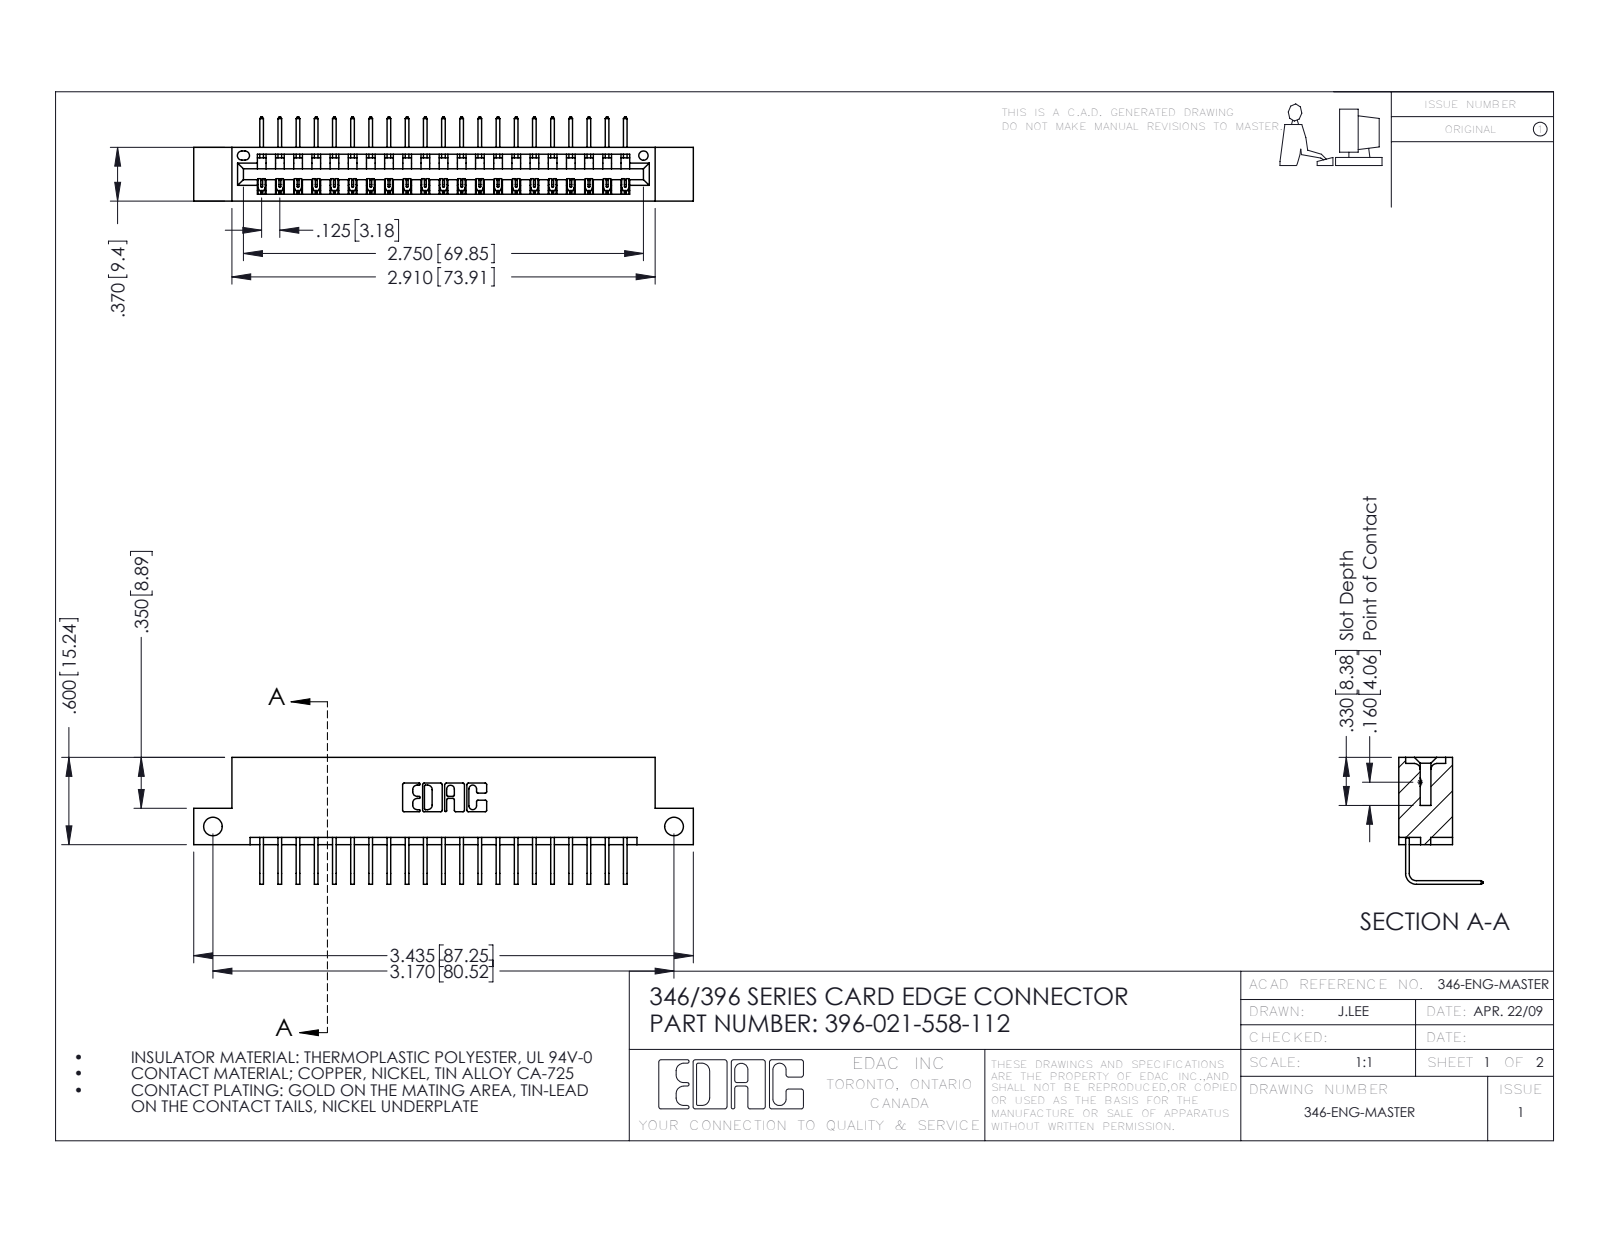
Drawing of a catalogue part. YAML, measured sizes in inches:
part_name: "345-292-001_558 Tail - 2; 346 Part_Flush Mounting Lugs - Side Mount; 396-021-558-112"
step_written_by: "SolidWorks 2016 (CONFIG_CONTROL_DESIGN)"
units: inches
bodies: {solids: 22, faces: 1382, planar: 958, cylindrical: 424, other: 0}
overall_size: [3.435, 0.873, 0.58]
volume: 0.5
surface_area: 15.94
round_holes:
  - {diameter: 0.128, count: 2}
  - {diameter: 0.064, count: 1}
partial_cylinders:
  - {radius: 0.006, count: 42}
  - {radius: 0.01, count: 22}
  - {radius: 0.007, count: 6}
  - {radius: 0.031, count: 6}
  - {radius: 0.026, count: 3}
  - {radius: 0.031, count: 2}
  - {radius: 0.04, count: 2}
  - {radius: 0.014, count: 1}
face_to_face_distances: [0.322, 0.048, 0.25, 0.37, 0.298, 0.025, 0.072, 0.148, 0.222, 0.1]
hole_center_spacings: [3.17]
